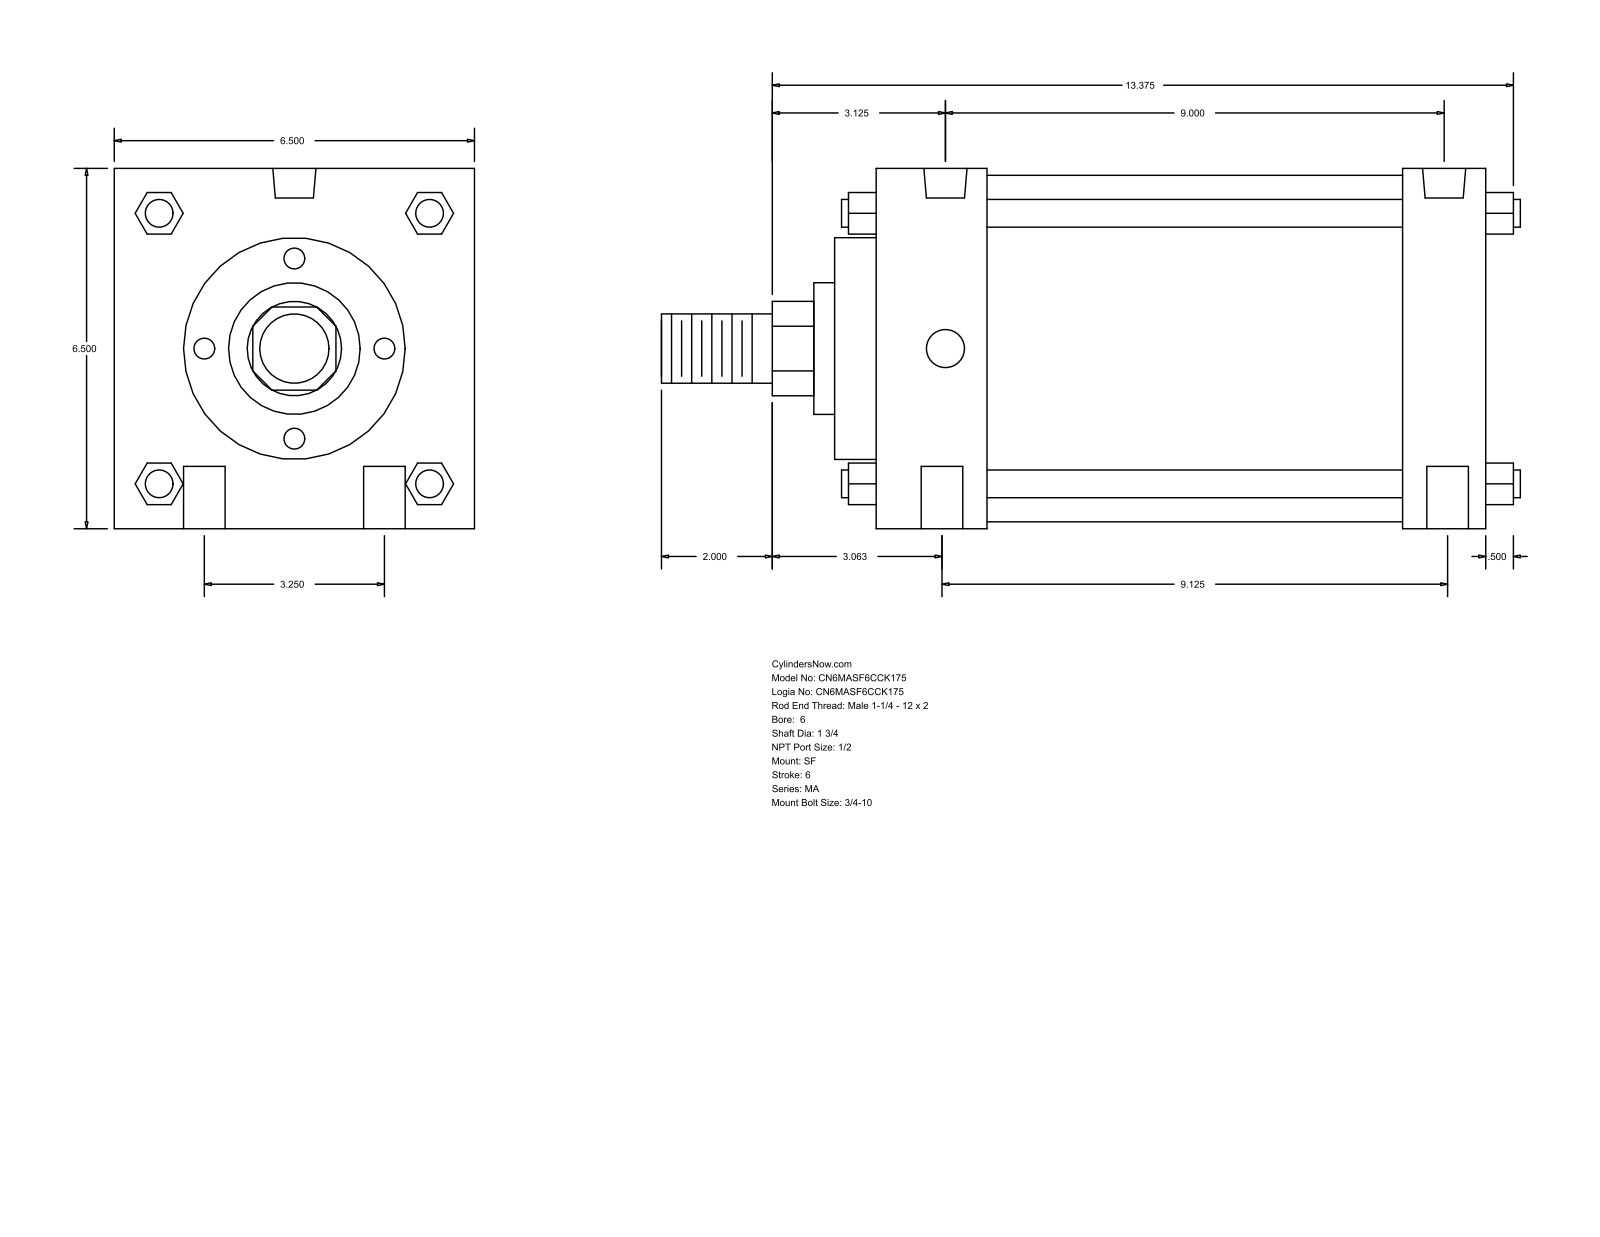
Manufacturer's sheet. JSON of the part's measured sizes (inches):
{"part_name": "MA_SF__0600_1.75", "step_written_by": "GSSL Pune (CONFIG_CONTROL_DESIGN)", "units": "inches", "bodies": {"solids": 0, "faces": 126, "planar": 95, "cylindrical": 31, "other": 0}, "overall_size": [15.5, 6.5, 6.5], "round_holes": [[0.75, 4], [0.687, 2], [0.778, 2]], "round_bosses_or_shafts": [[0.5, 4], [6.25, 1], [4, 1], [2.375, 1], [1.75, 1], [1.25, 1]], "partial_cylinders_radius": [[0.852, 1]], "face_to_face_distances": [6.5, 11, 0.75, 2, 9.5, 1.5, 7.5, 9, 2.75, 10.25], "hole_center_spacings": [1.626, 3.25, 9, 9.125, 9.207, 9.207, 9.686]}
